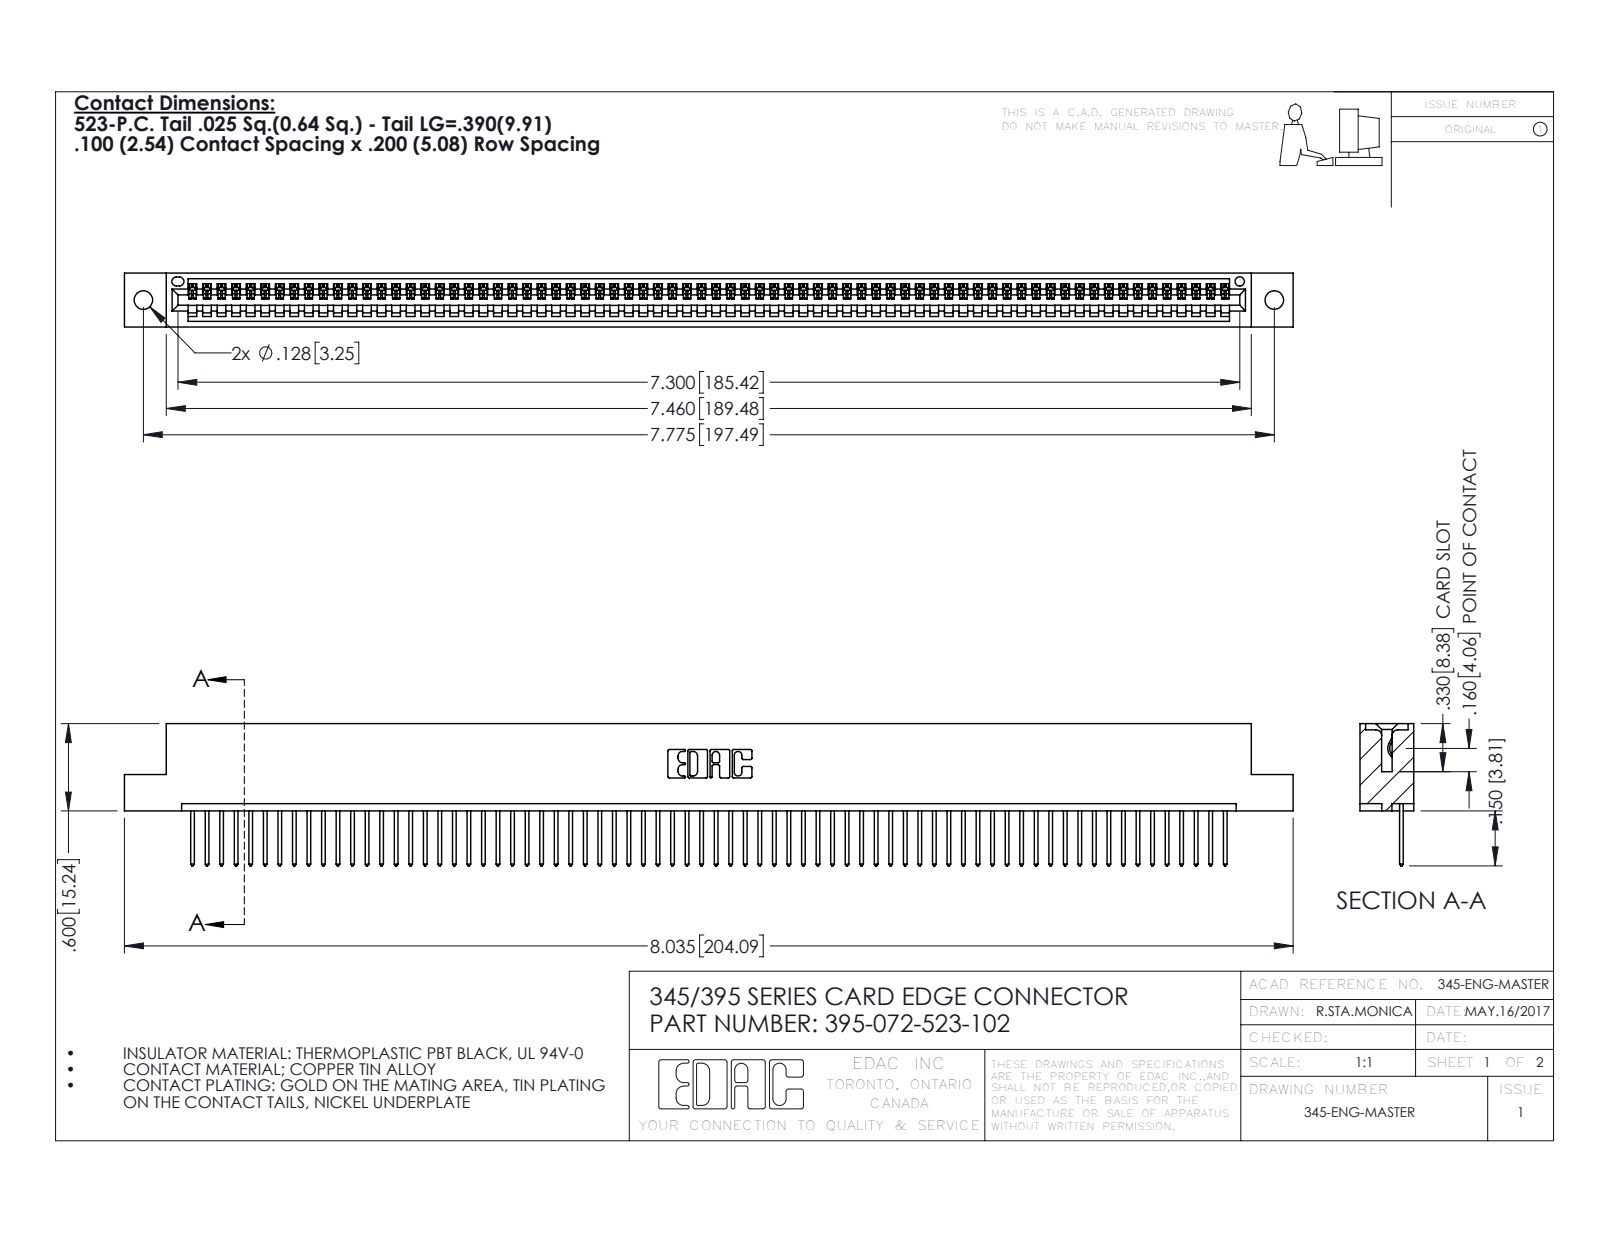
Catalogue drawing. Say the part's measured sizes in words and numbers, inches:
The part is named "345 Part_Flush Mounting Lugs - 0.128 Dia; 395-072-523-102; 345-292-001_345-293-123". Its 3-D file was written by "SolidWorks 2016 (CONFIG_CONTROL_DESIGN)". It is 73 solids with 4302 faces: 2960 planar, 1342 cylindrical and 0 other. Overall it measures 8.035 by 0.977 by 0.37 inches. Its volume is 1.194 cubic inches and its surface area 40.63 square inches. Round holes: 2 of diameter 0.128, 1 of diameter 0.064. Partial cylindrical surfaces (rounded edges, fillets, slot ends): 144 of radius 0.006, 144 of radius 0.01, 22 of radius 0.01, 6 of radius 0.007, 6 of radius 0.031, 3 of radius 0.026, 2 of radius 0.031, 2 of radius 0.04. The main face-to-face distances are 0.298, 0.072, 0.37, 0.2, 0.098, 0.272, 0.025, 0.225, 0.149, 0.072. The hole center spacings are 0.27, 7.539, 7.775.
